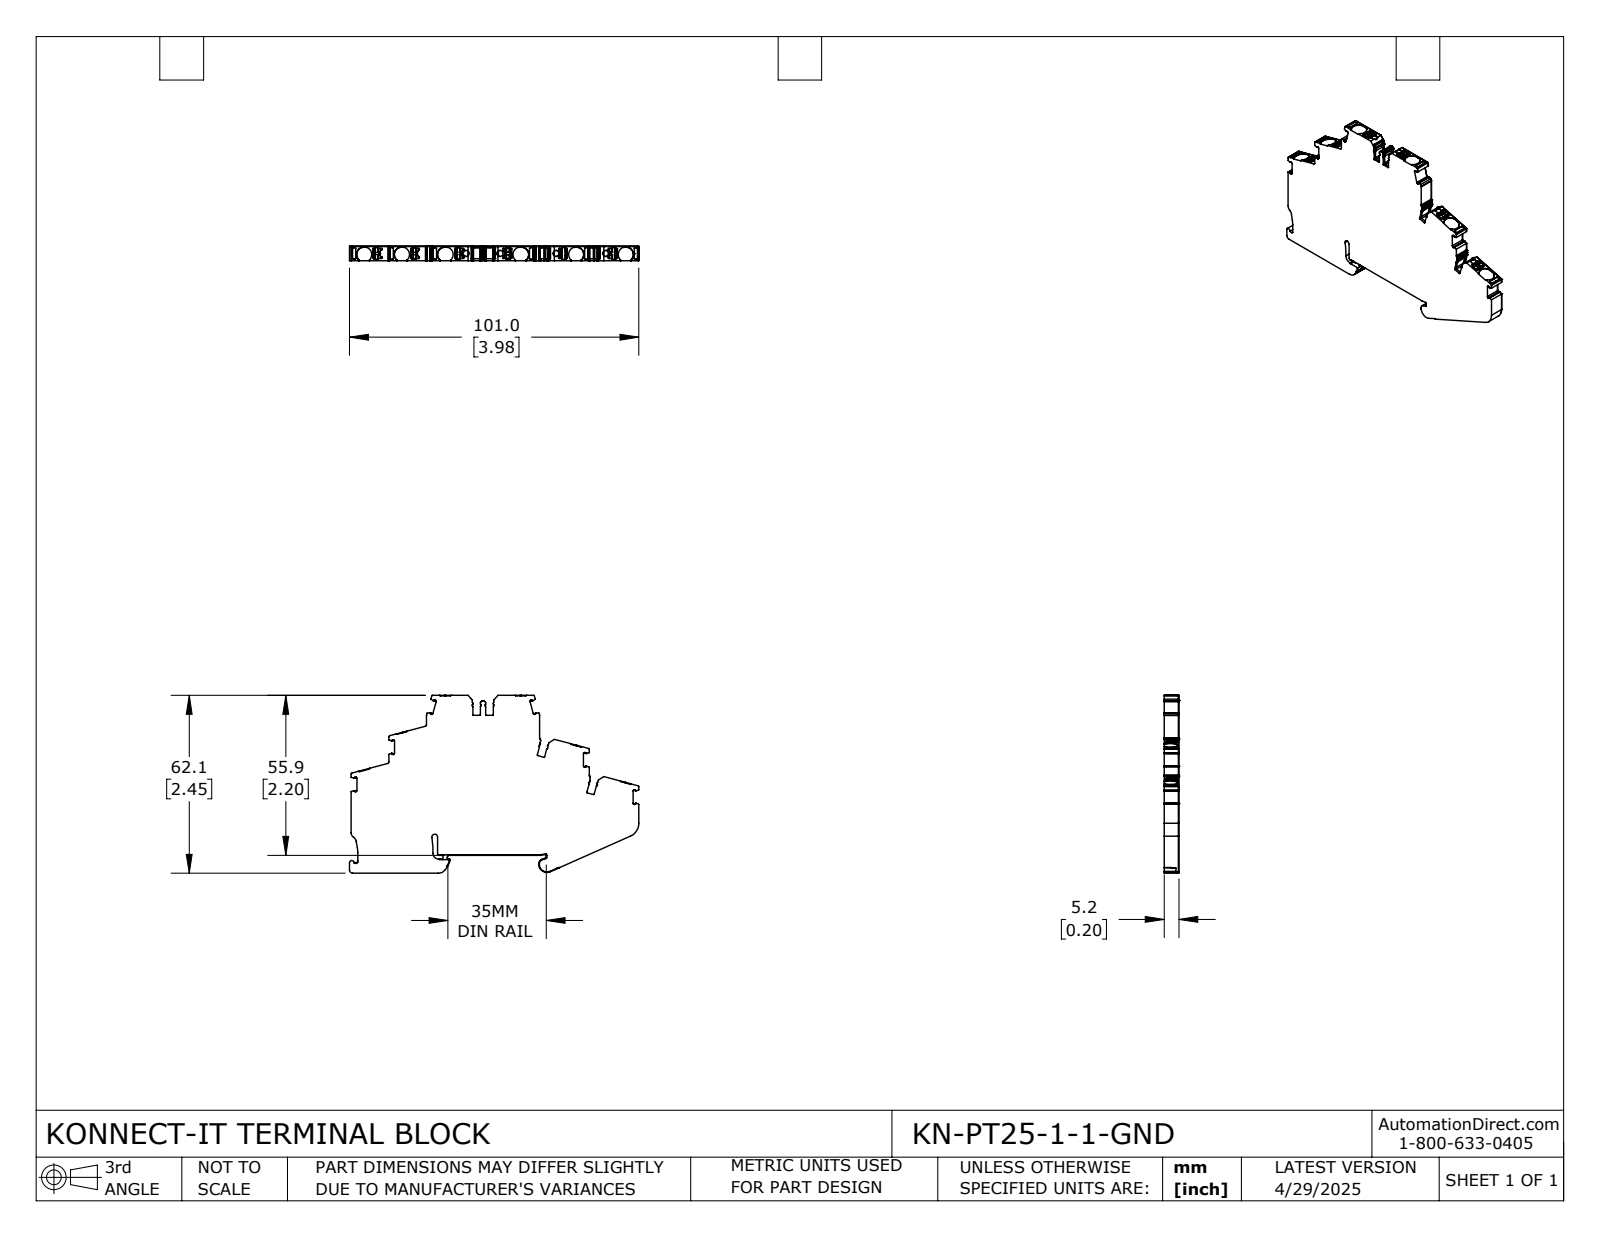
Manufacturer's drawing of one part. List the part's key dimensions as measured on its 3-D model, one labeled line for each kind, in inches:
Part name (STEP PRODUCT): KN-PT25-1-1-GND
STEP written by: SolidWorks 2024 (CONFIG_CONTROL_DESIGN)
Units: inches
Bodies: 8 solids, 1470 faces (670 planar, 651 cylindrical, 149 other)
Overall size (bounding box): 3.977 × 2.445 × 0.203
Volume: 1.393 in³ · Surface area: 19.17 in²
Round holes (diameter × count): ⌀0.083 ×4
Partial cylindrical surfaces — rounded edges, fillets, slot ends (radius × count): R0.008 ×137, R0.004 ×55, R0.012 ×53, R0.02 ×39, R0.006 ×36, R0.016 ×25, R0.039 ×16, R0.024 ×14
Main face-to-face distances: 0.203, 0.053, 0.1, 0.102, 0.15, 0.047, 2.191, 0.246, 0.079, 0.035
Hole centre spacings: 0.466, 0.792
